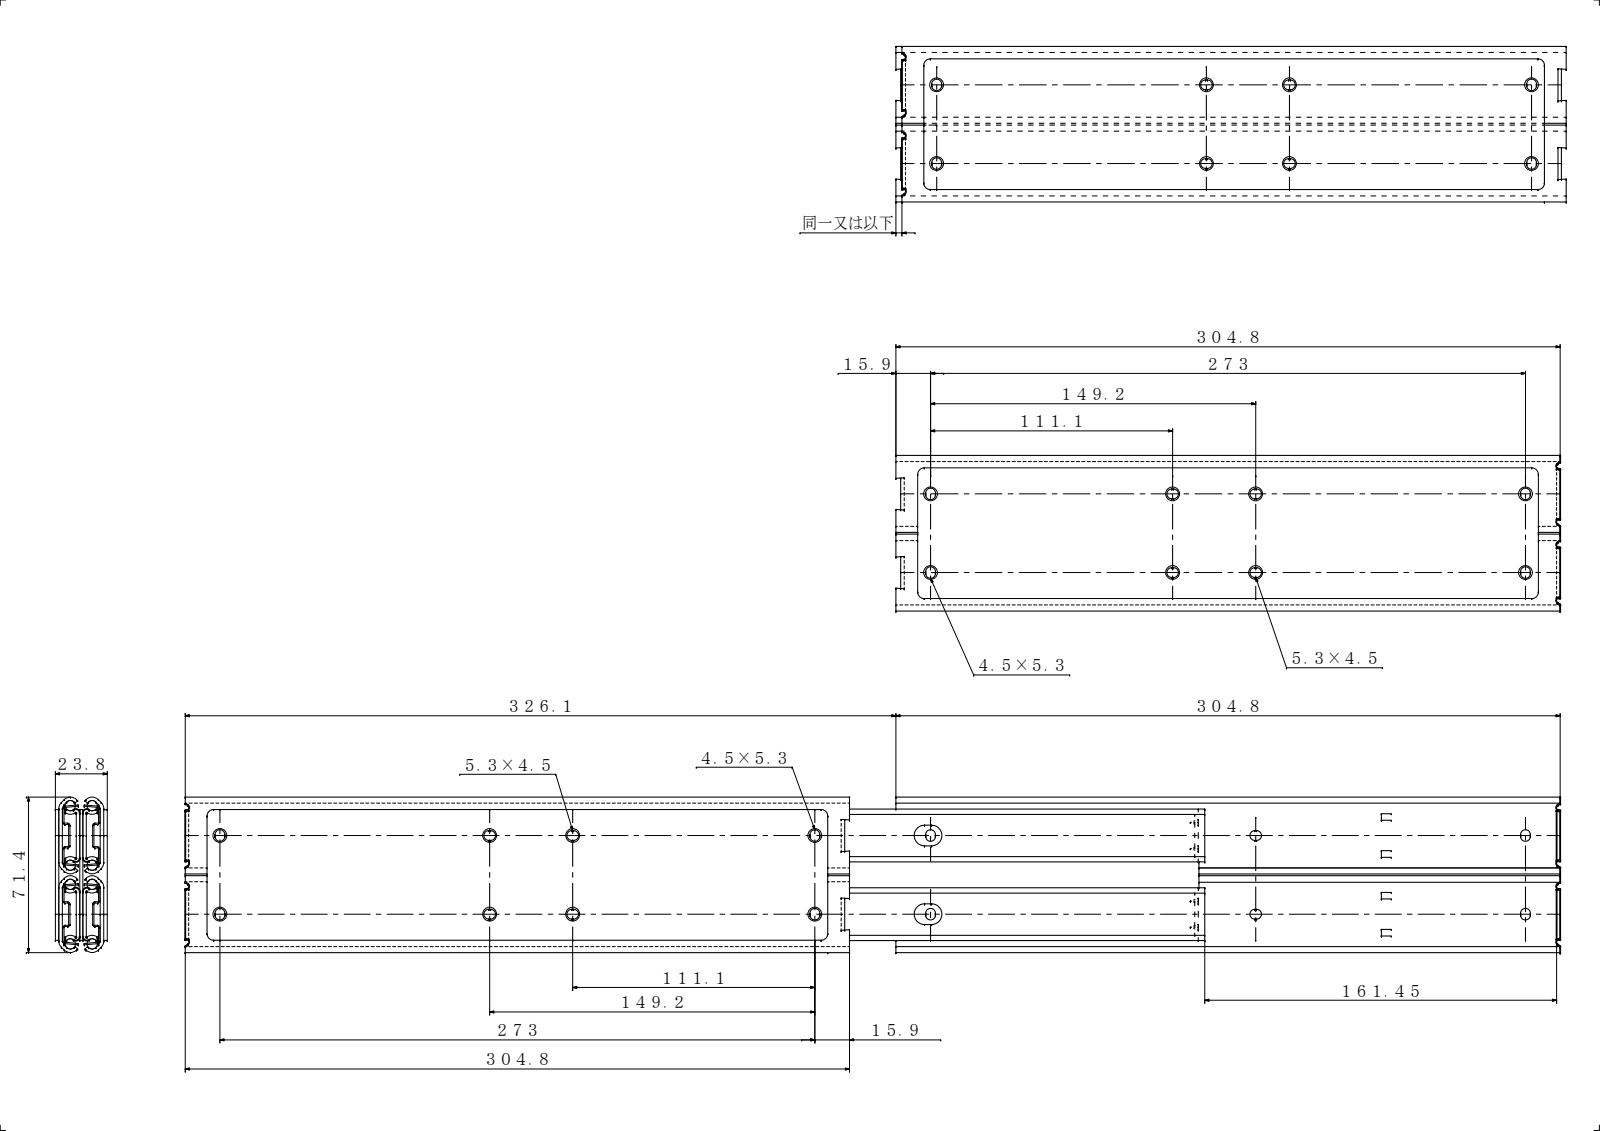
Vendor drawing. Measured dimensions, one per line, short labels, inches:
name: IM-継板; OM-継板; IM-3551-12; 3551-12 (+1 more)
written by: SolidWorks 2019 (CONFIG_CONTROL_DESIGN)
unit: in
bodies: 11 solids, 568 faces (262 planar, 306 cylindrical, 0 other)
size: 24.839 × 2.811 × 0.937
volume: 14.07 in³; area: 475.5 in²
holes: 20× ⌀0.252, 2× ⌀0.256
rounds: 32× R0.089, 24× R0.016, 20× R0.157, 16× R0.039, 16× R0.118, 14× R0.079, 12× R0.187, 8× R0.008
face distances: 0.063, 0.433, 0.378, 0.811, 0.496, 0.315, 0.441, 0.874, 0.055, 0.126
hole spacings: 1.421, 1.374, 1.5, 1.977, 2.067, 3, 3.32, 3.465
